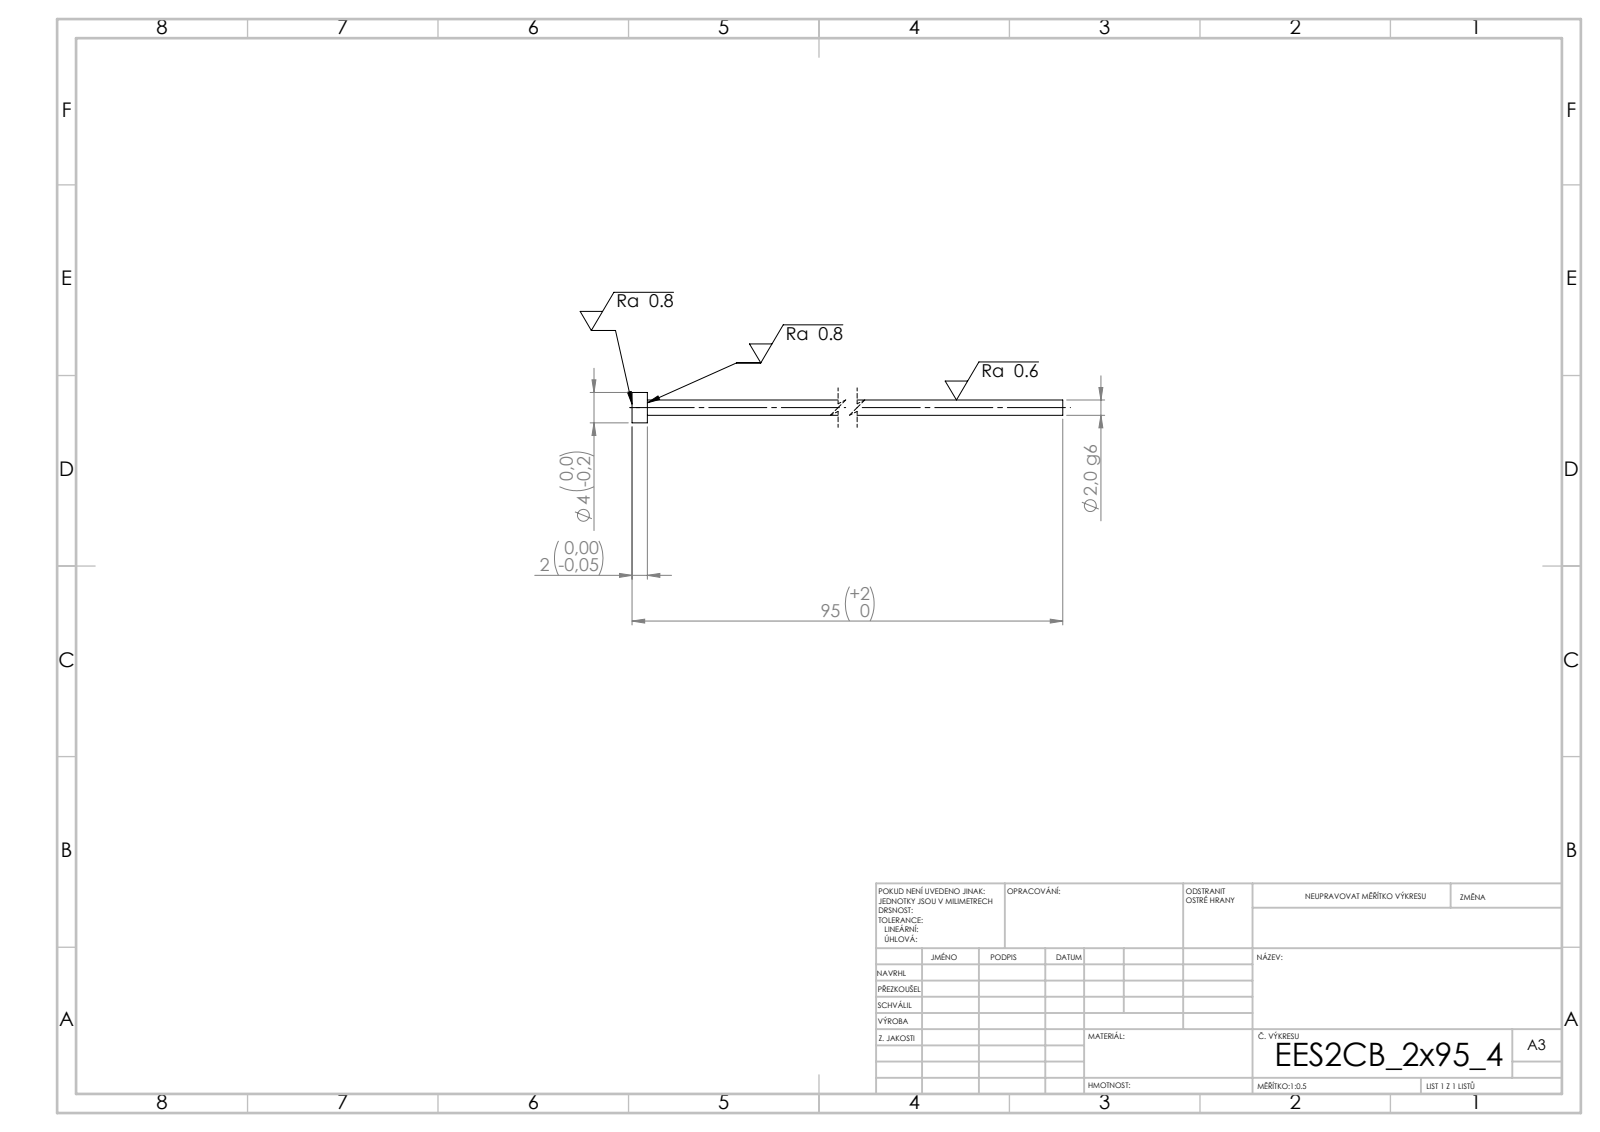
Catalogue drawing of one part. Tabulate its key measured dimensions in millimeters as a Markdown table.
| quantity | value |
| --- | --- |
| STEP written by | SolidWorks 2019 (CONFIG_CONTROL_DESIGN) |
| units | millimeters |
| bodies | 1 solid, 7 faces (3 planar, 4 cylindrical, 0 other) |
| overall size | 95.4 × 4 × 4 |
| volume | 319 mm³ |
| surface area | 637 mm² |
| round bosses / shafts (diameter × count) | 4 × 1, 2 × 1 |
| main face-to-face distances | 2, 95.4, 93.4 |
